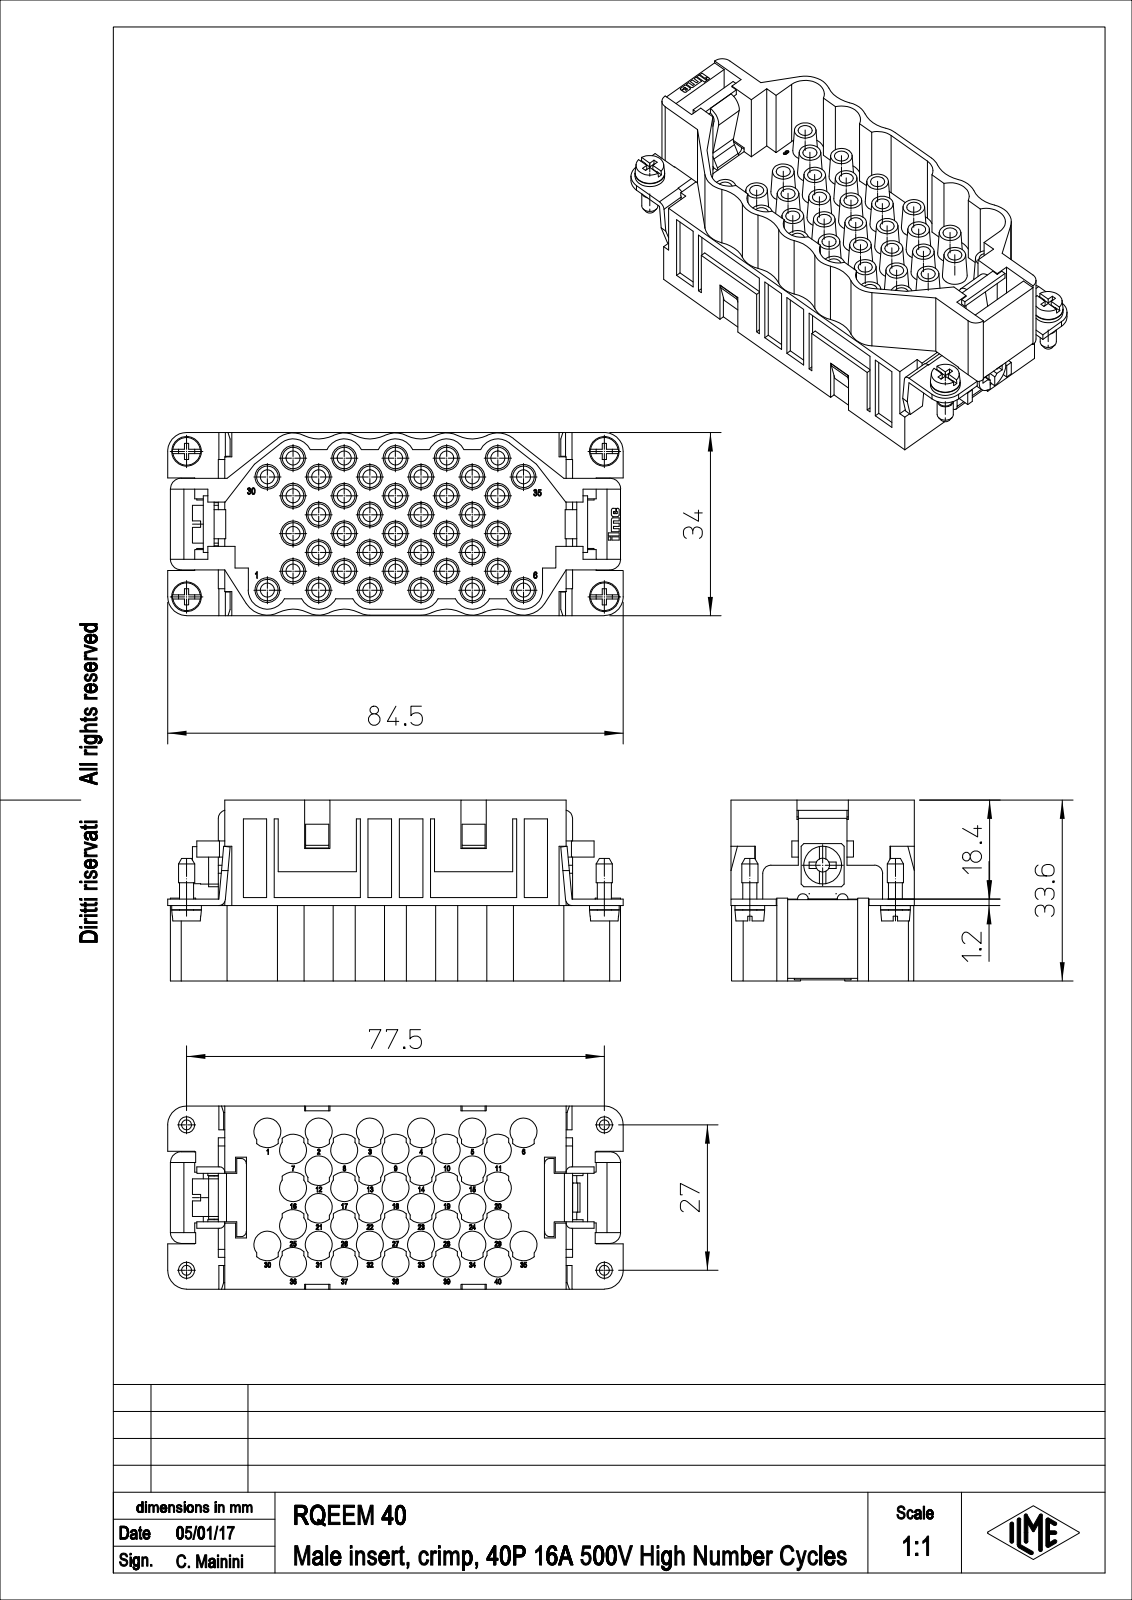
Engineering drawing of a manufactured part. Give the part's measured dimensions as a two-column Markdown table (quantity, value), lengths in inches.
| quantity | value |
| --- | --- |
| part name | RQEEM_40 |
| STEP written by | PTC Creo Elements/Direct Modeling 19.0E 27-Jun-2016 (C) Parametric Technology GmbH (AUTOMOTIVE_DESIGN) |
| units | inches |
| bodies | 1 solid, 1189 faces (799 planar, 292 cylindrical, 98 other) |
| overall size | 3.327 × 1.339 × 1.323 |
| volume | 2.838 in³ |
| surface area | 39.88 in² |
| round holes (diameter × count) | 0.102 × 40, 0.11 × 4, 0.102 × 1, 0.118 × 1 |
| round bosses / shafts (diameter × count) | 0.217 × 4, 0.118 × 4, 0.102 × 4, 0.276 × 1, 0.236 × 1 |
| partial cylindrical surfaces (radius × count) | 0.098 × 42, 0.118 × 40, 0.039 × 12, 0.14 × 11, 0.183 × 11, 0.243 × 8, 0.079 × 6, 0.047 × 4 |
| main face-to-face distances | 0.079, 0.047, 0.732, 1.303, 0.654, 0.035, 0.299, 0.591, 1.339, 0.098 |
| hole center spacings | 0.232, 0.578, 0.465, 0.666, 0.374, 0.454, 0.797, 0.945 |
